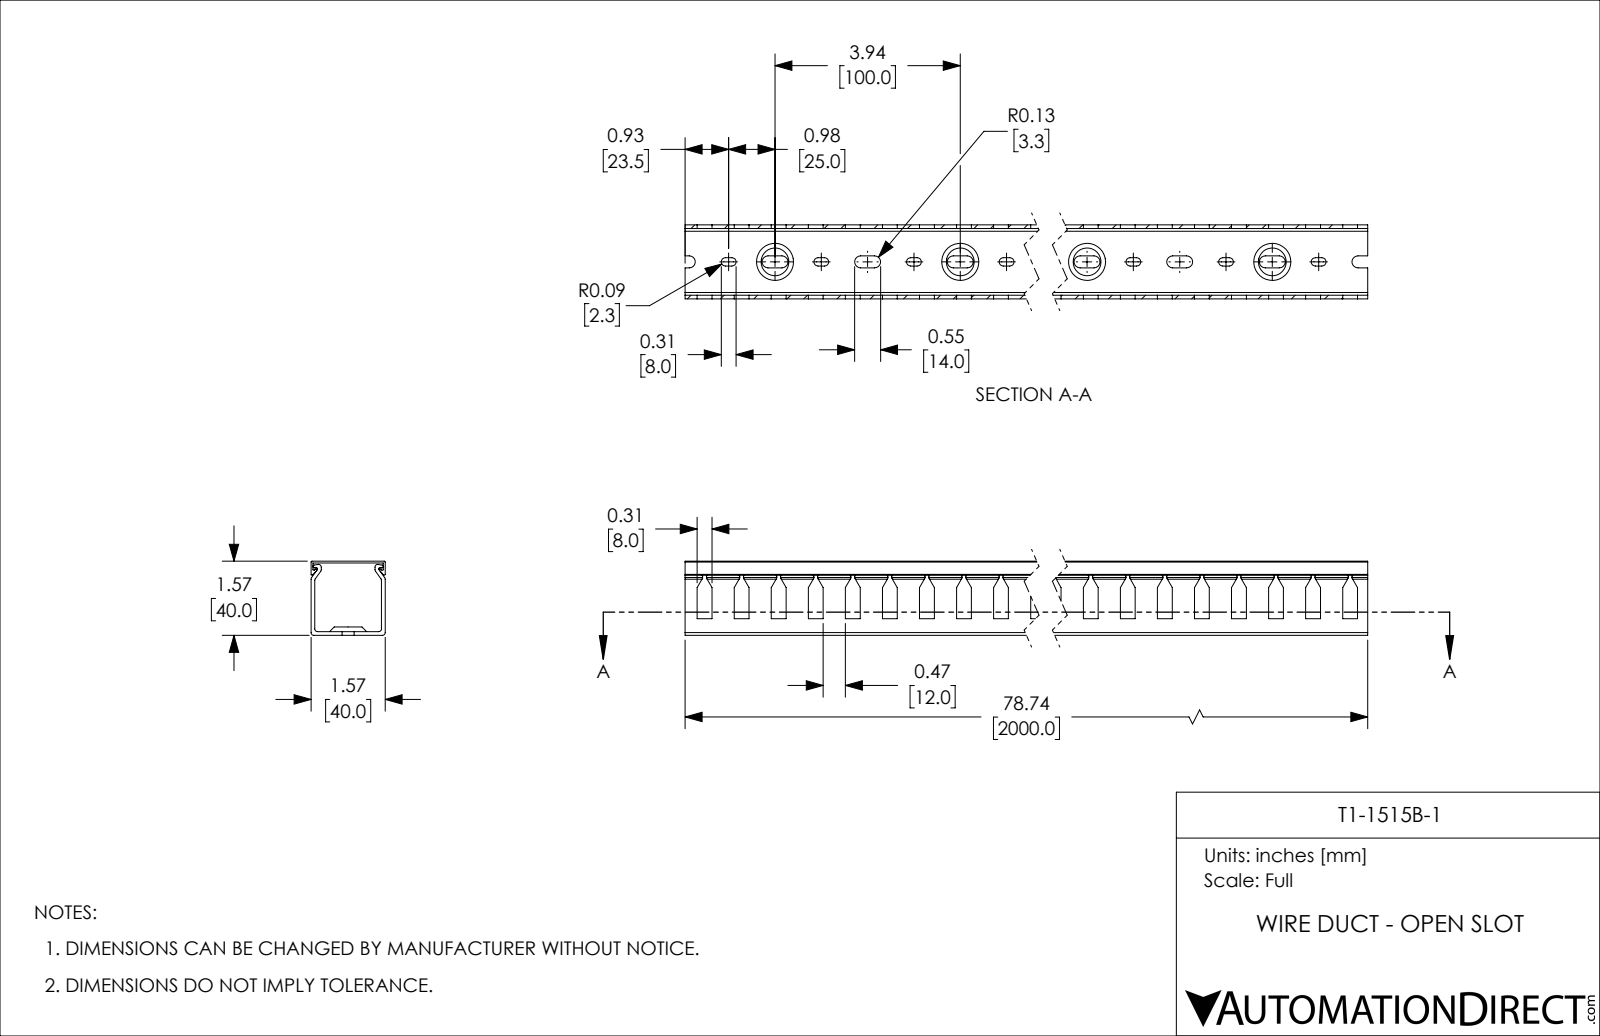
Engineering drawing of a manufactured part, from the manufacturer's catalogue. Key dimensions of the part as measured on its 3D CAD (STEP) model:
Part name (STEP PRODUCT): T1-1515B-1
STEP written by: SolidWorks 2021 (CONFIG_CONTROL_DESIGN)
Units: millimetres
Bodies: 2 solids, 1005 faces (534 planar, 431 cylindrical, 40 other)
Overall size (bounding box): 2000 × 40 × 40
Volume: 581 112 mm³ · Surface area: 696 182 mm²
Partial cylindrical surfaces — rounded edges, fillets, slot ends (radius × count): R2.25 ×80, R3.25 ×80, R1.5 ×12, R0.5 ×8, R0.75 ×6
Main face-to-face distances: 2, 38, 40, 1, 39, 37, 36, 4.5, 34.5, 5.5
